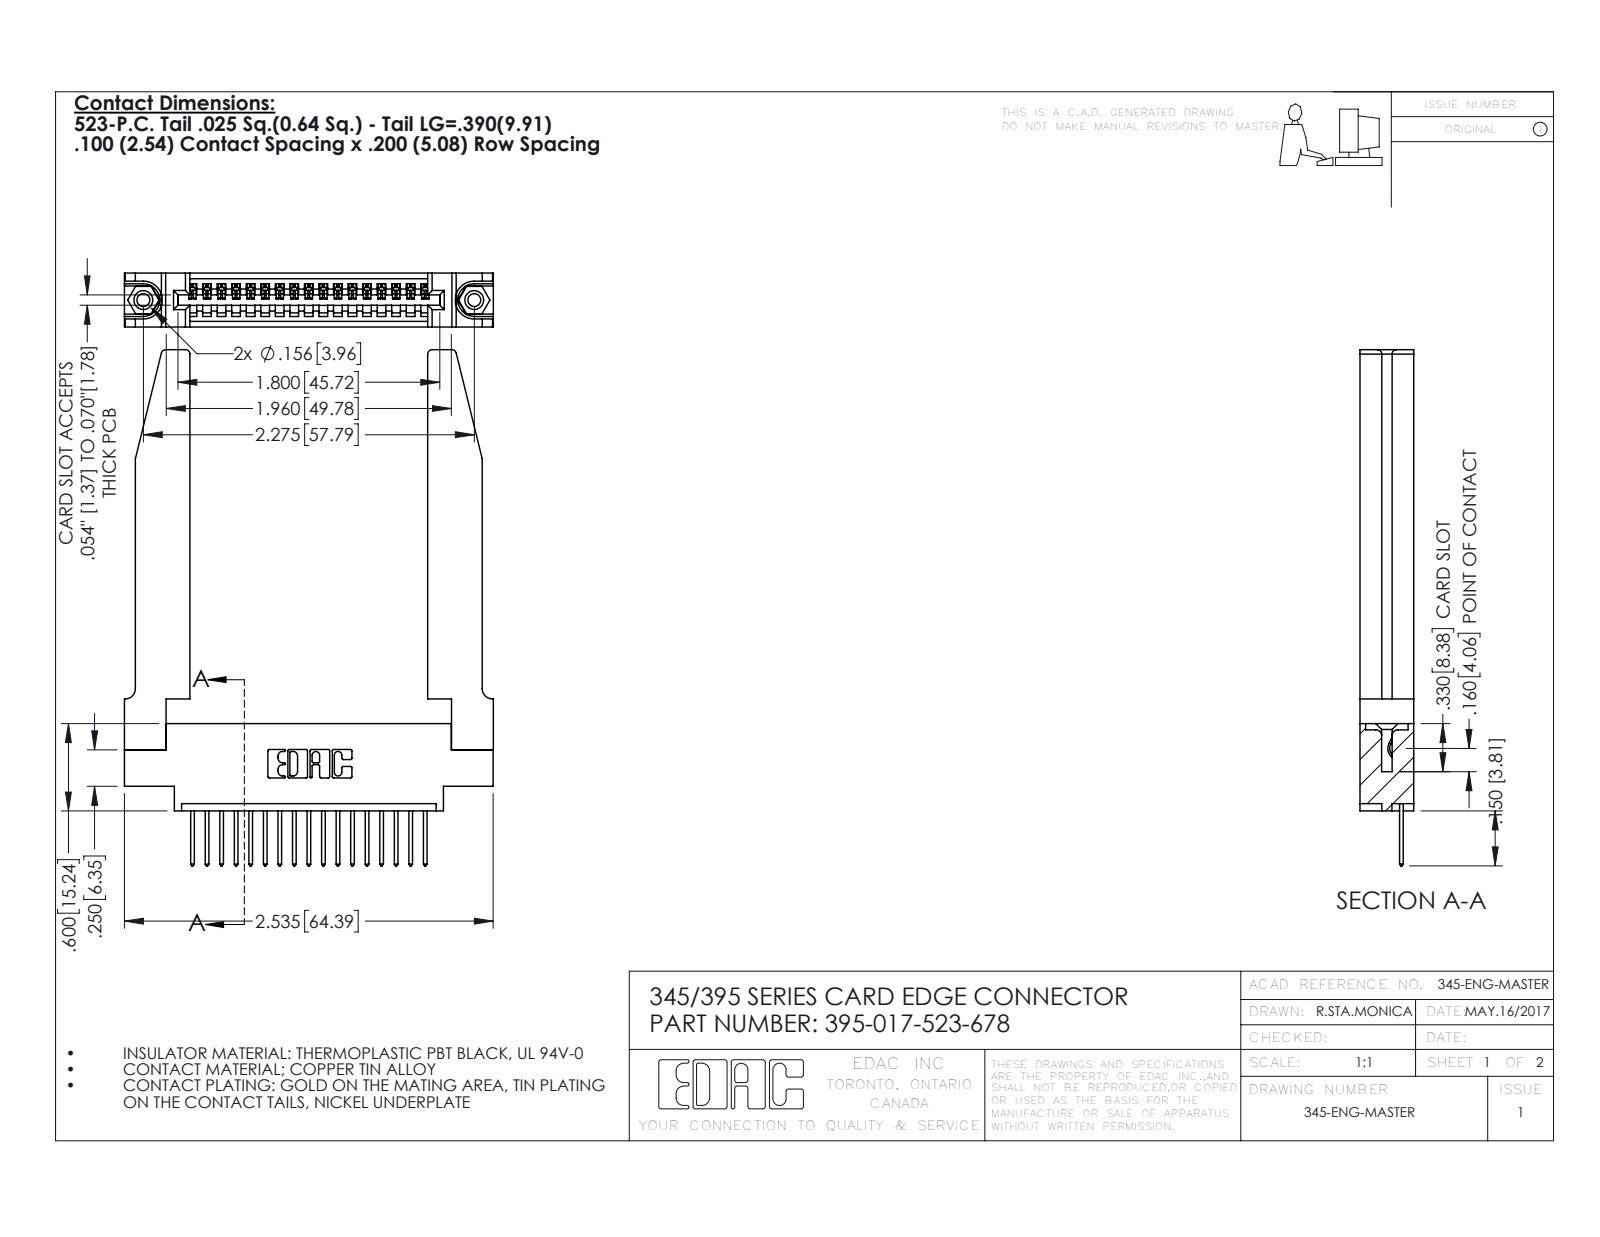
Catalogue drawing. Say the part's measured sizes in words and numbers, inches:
The part is named "395-017-523-678; 345-220-078_345-220-078; 345-292-001_345-293-123; 345 Part_0.170 Offset - 0.156 Dia-TH (+1 more)". Its 3-D file was written by "SolidWorks 2016 (CONFIG_CONTROL_DESIGN)". It is 22 solids with 1350 faces: 906 planar, 392 cylindrical and 52 other. Overall it measures 3.547 by 2.536 by 0.37 inches. Its volume is 0.828 cubic inches and its surface area 22.24 square inches. Round holes: 2 of diameter 0.089, 2 of diameter 0.125, 2 of diameter 0.156, 1 of diameter 0.064. Round bosses or shafts: 2 of diameter 0.155. Partial cylindrical surfaces (rounded edges, fillets, slot ends): 34 of radius 0.006, 34 of radius 0.01, 22 of radius 0.01, 8 of radius 0.03, 6 of radius 0.007, 6 of radius 0.031, 3 of radius 0.026, 2 of radius 0.031. The main face-to-face distances are 0.37, 0.072, 0.298, 0.148, 0.15, 0.098, 0.272, 0.025, 0.2, 0.22. The hole center spacings are 0.27, 2.041, 2.275.
